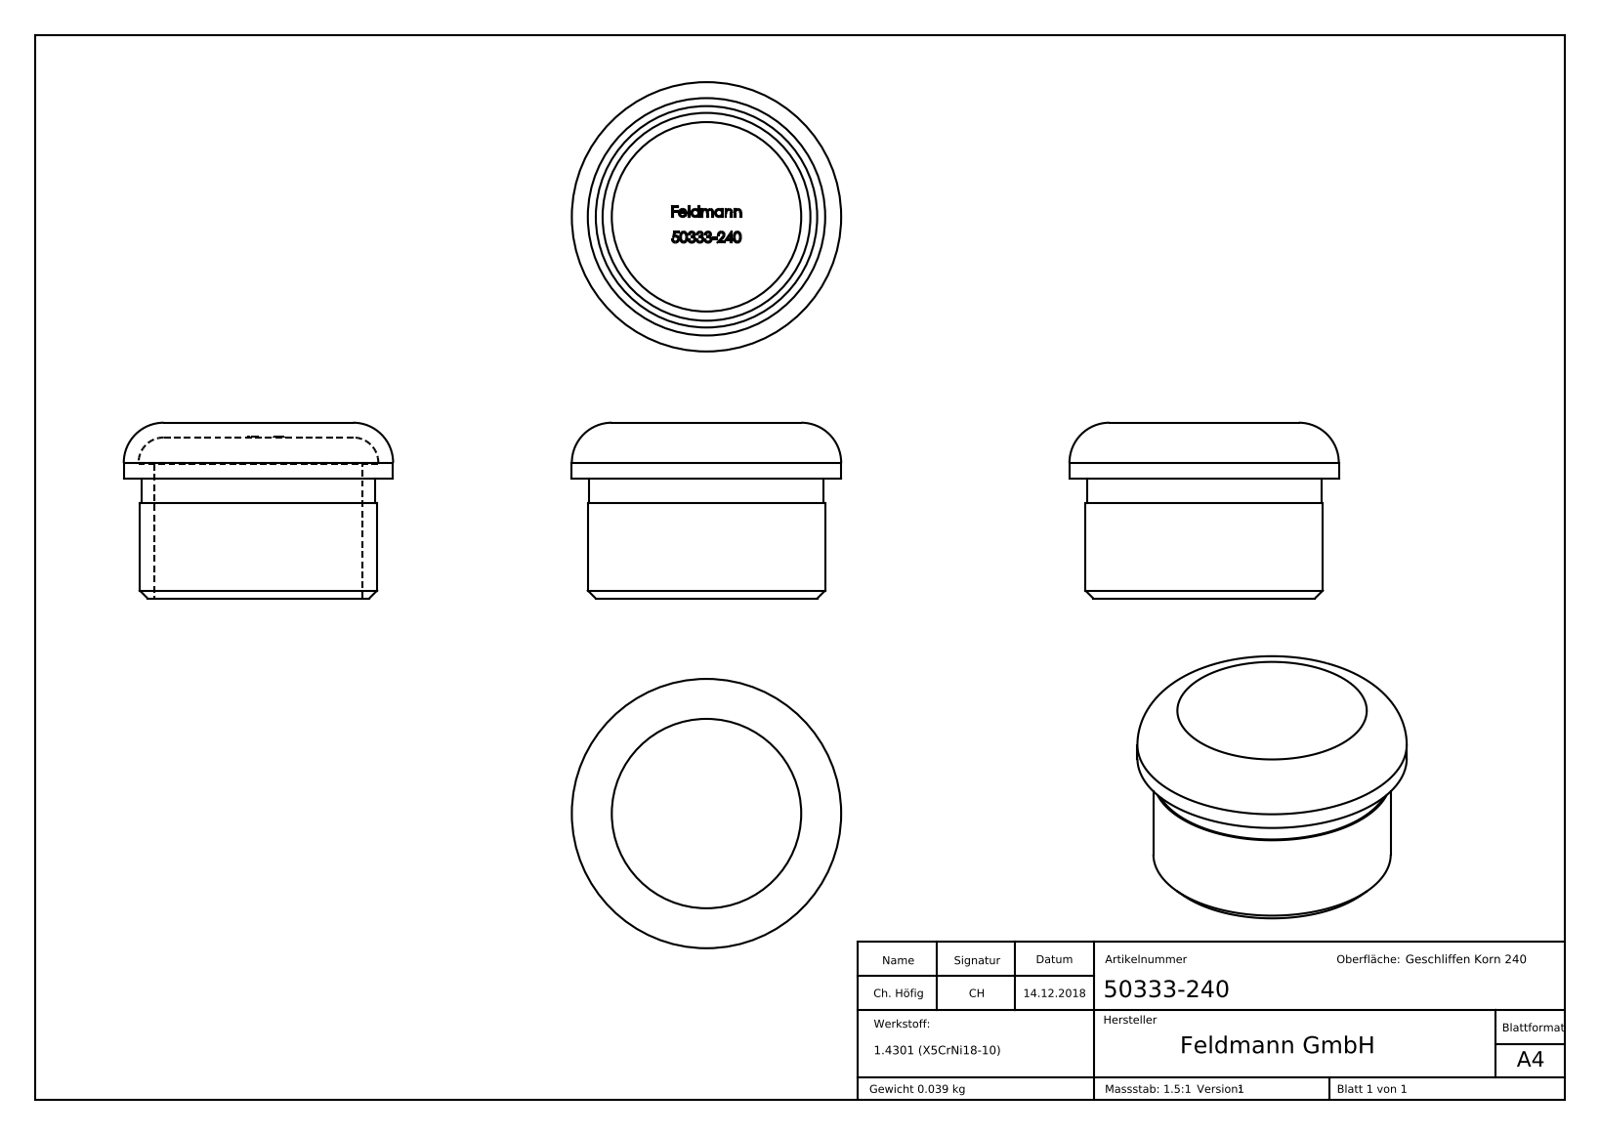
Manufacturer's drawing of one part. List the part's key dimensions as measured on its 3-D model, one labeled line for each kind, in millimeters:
Part name (STEP PRODUCT): 50333-240
STEP written by: SolidWorks 2015 (CONFIG_CONTROL_DESIGN)
Units: millimetres
Bodies: 1 solid, 259 faces (121 planar, 10 cylindrical, 128 other)
Overall size (bounding box): 33.7 × 33.7 × 22
Volume: 4 916 mm³ · Surface area: 5 581 mm²
Round holes (diameter × count): ⌀26 ×1, ⌀30 ×1
Round bosses / shafts (diameter × count): ⌀33.7 ×1, ⌀29.7 ×1, ⌀29.3 ×1
Main face-to-face distances: 1.85, 5.15, 7, 3.3, 15, 16.85, 20.15, 22, 12, 3
